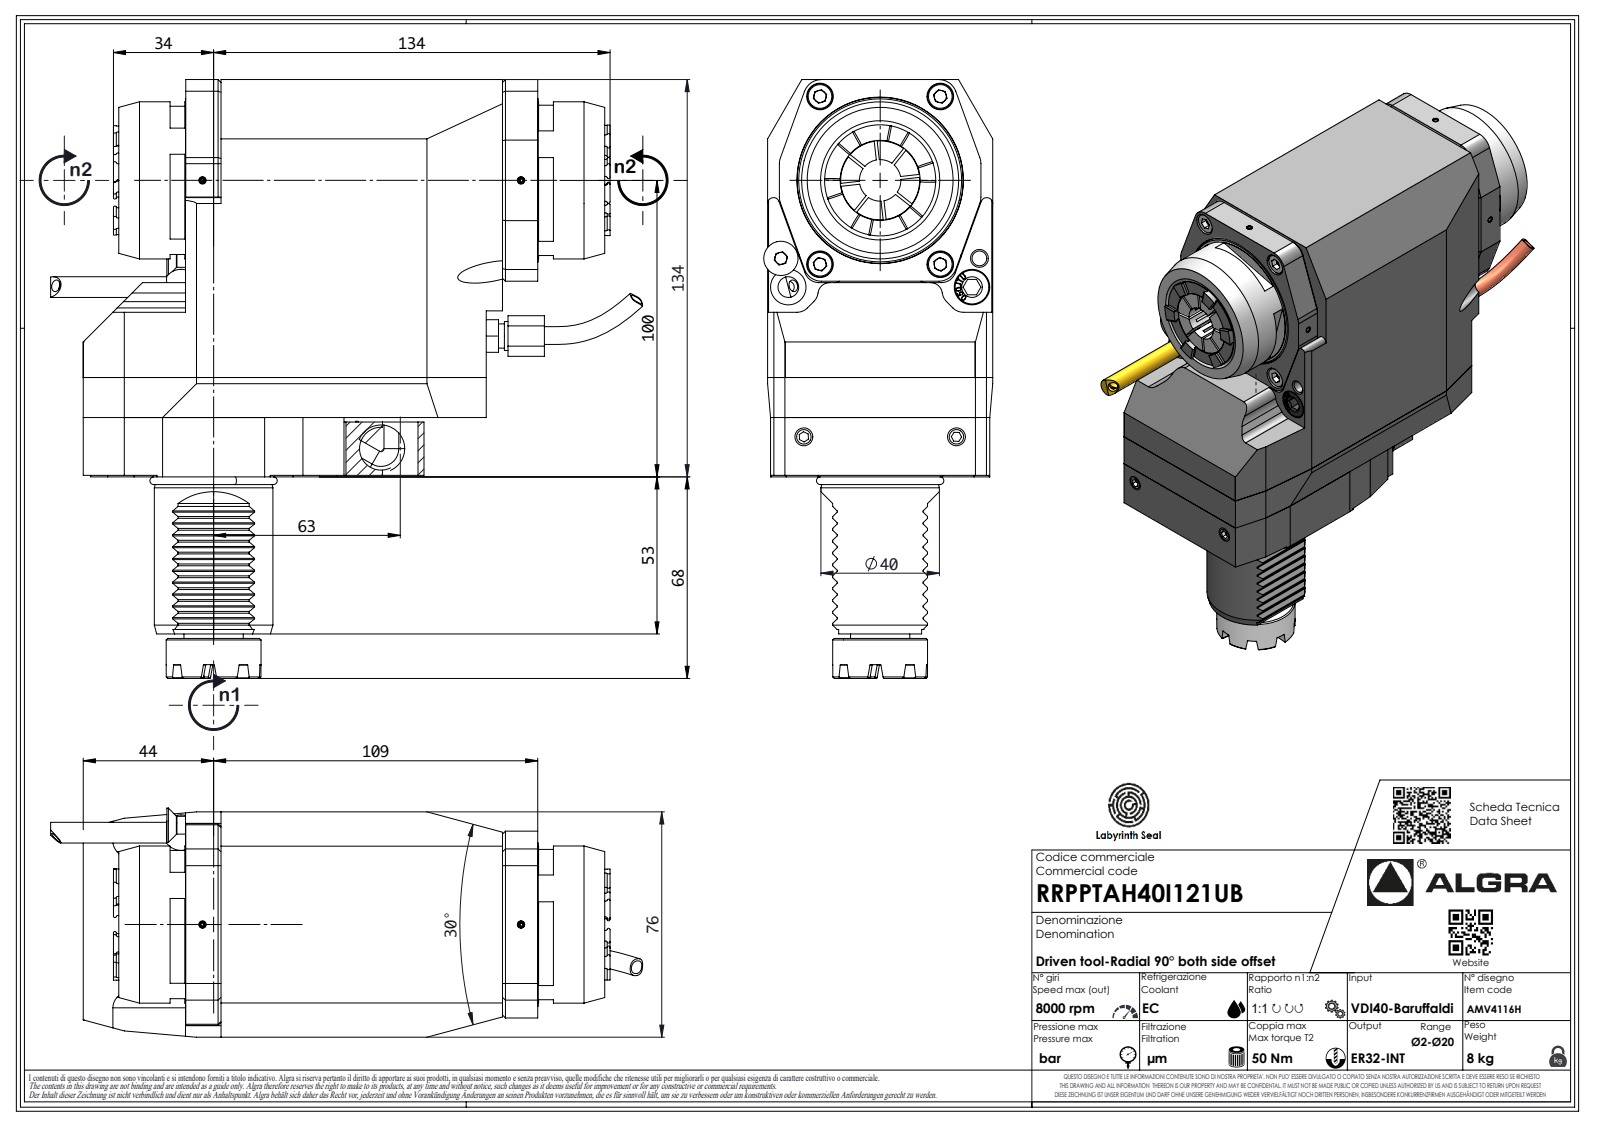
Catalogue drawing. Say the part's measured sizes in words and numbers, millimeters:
The part is named "RRPPTAH40I121UB". Its 3-D file was written by "SolidWorks 2023 (AUTOMOTIVE_DESIGN)". It is 1 solid with 694 faces: 496 planar, 103 cylindrical and 95 other. Overall it measures 202 by 199.81 by 76 millimeters. Its volume is 1 320 000 cubic millimeters and its surface area 94 062 square millimeters. Round holes: 1 of diameter 2.1, 1 of diameter 4, 1 of diameter 17.2. Round bosses or shafts: 1 of diameter 53, 1 of diameter 40, 1 of diameter 38.7, 1 of diameter 32, 1 of diameter 20, 1 of diameter 9.8, 1 of diameter 8.15, 1 of diameter 7. Partial cylindrical surfaces (rounded edges, fillets, slot ends): 22 of radius 0.3, 12 of radius 0.2, 10 of radius 6, 7 of radius 0.33, 7 of radius 0.52, 7 of radius 3.7, 6 of radius 5, 3 of radius 2. The main face-to-face distances are 76, 134, 20, 114, 0.5, 22.6, 141.4, 12, 68.5, 133.5.
